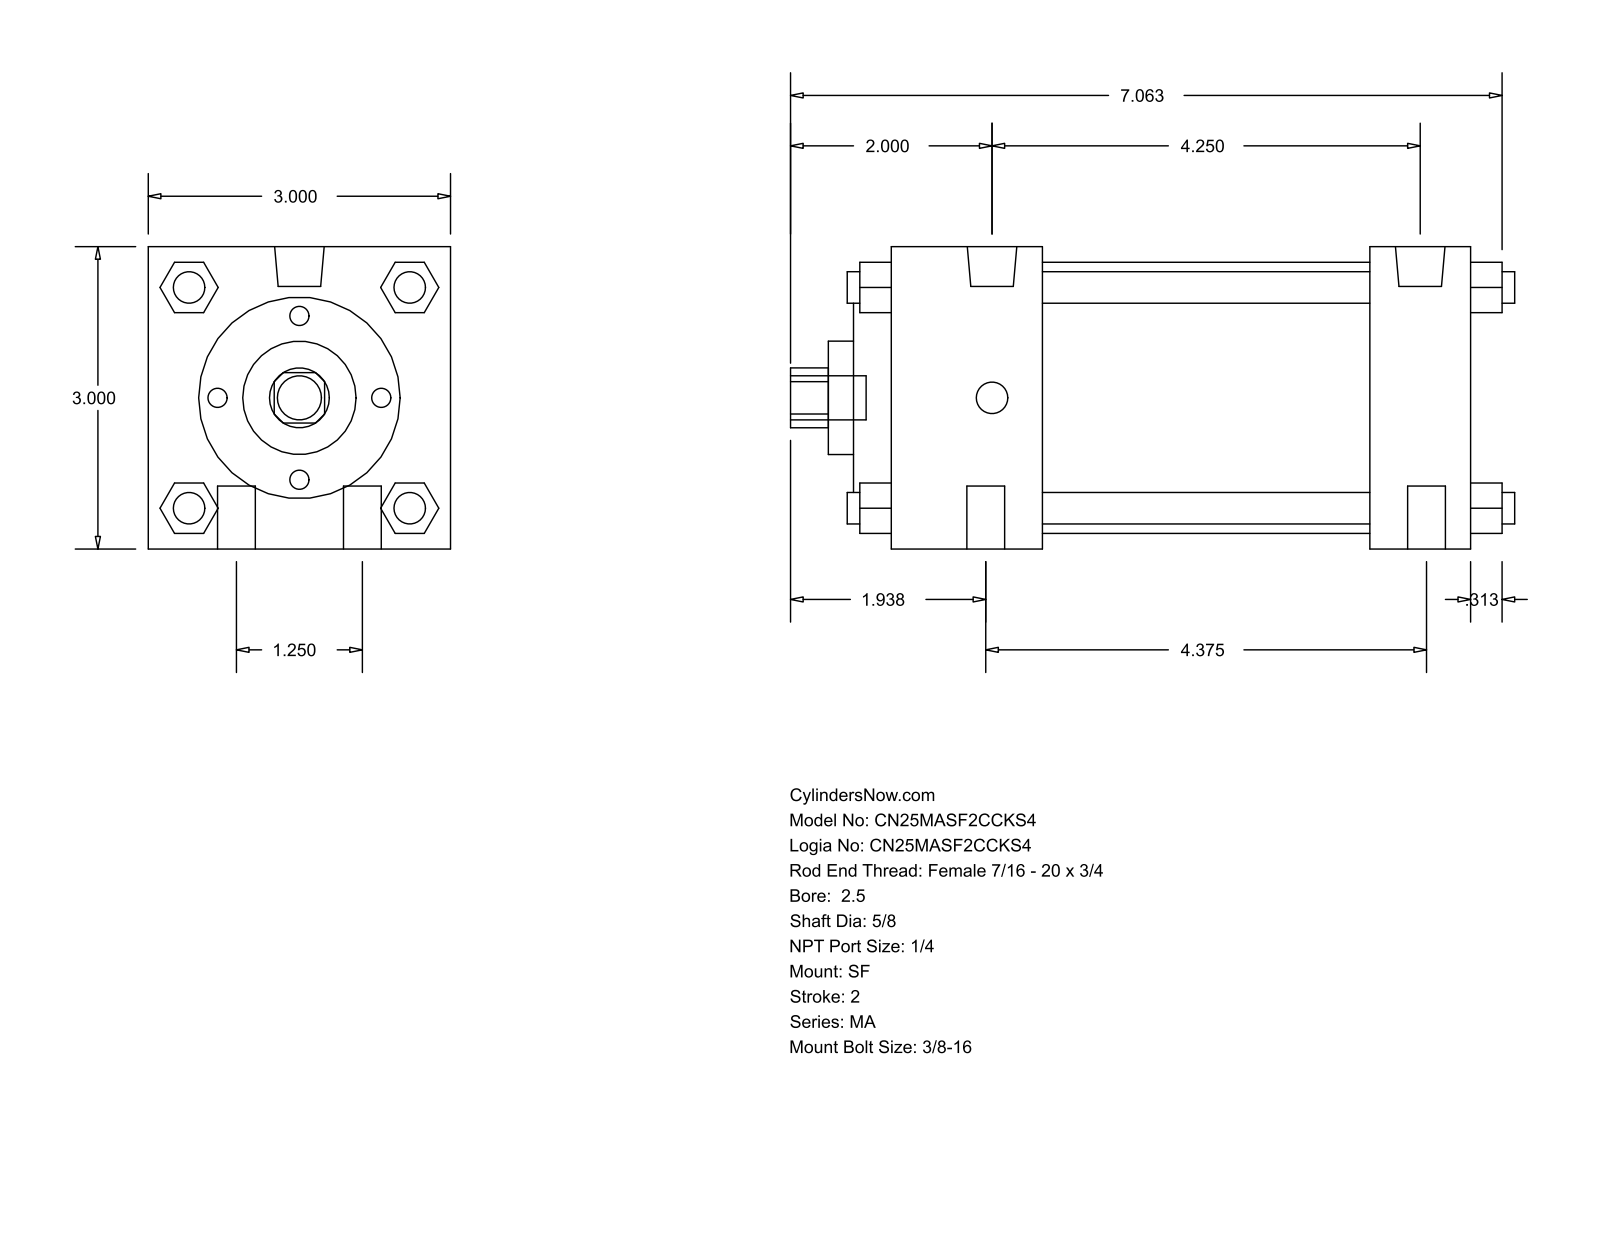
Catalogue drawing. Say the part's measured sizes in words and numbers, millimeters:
The part is named "MA_SF__0250_0.625". Its 3-D file was written by "GSSL Pune (CONFIG_CONTROL_DESIGN)". It is 0 solids with 126 faces: 95 planar, 31 cylindrical and 0 other. Overall it measures 182.56 by 76.2 by 76.2 millimeters. Round holes: 1 of diameter 15.88, 1 of diameter 28.57, 1 of diameter 50.8, 1 of diameter 68.33. Round bosses or shafts: 6 of diameter 7.94, 4 of diameter 9.53, 2 of diameter 12.49, 1 of diameter 11.11. Partial cylindrical surfaces (rounded edges, fillets, slot ends): 1 of radius 7.54. The main face-to-face distances are 76.2, 146.05, 25.4, 120.65, 38.1, 82.55, 107.95, 12.7, 9.52, 47.62.
